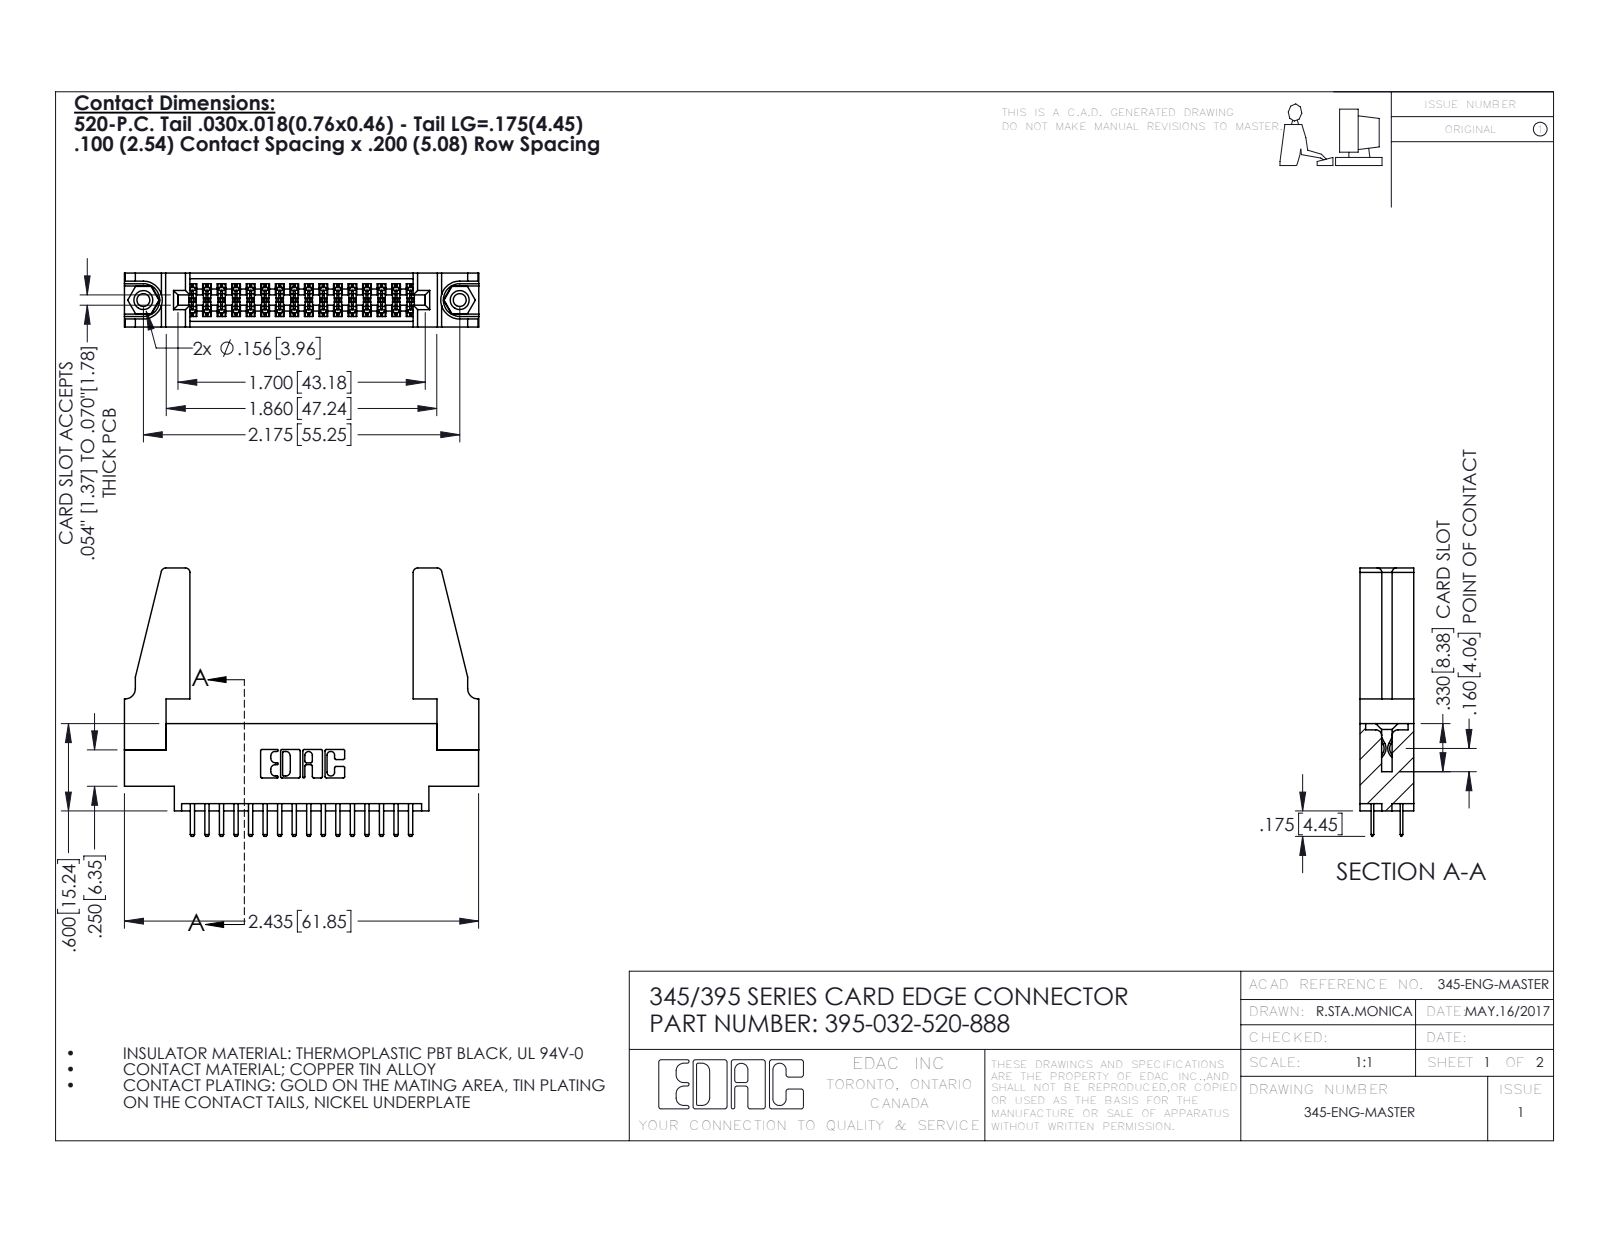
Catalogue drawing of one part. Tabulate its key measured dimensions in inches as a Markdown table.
| quantity | value |
| --- | --- |
| part name | 345-250-001_345-250-001-102; 345 Part_0.170 Offset - 0.156 Dia-TH; 345-292-001_345-293-120; 395-032-520-888 (+1 more) |
| STEP written by | SolidWorks 2016 (CONFIG_CONTROL_DESIGN) |
| units | inches |
| bodies | 37 solids, 1982 faces (1276 planar, 690 cylindrical, 16 other) |
| overall size | 2.436 × 1.845 × 0.37 |
| volume | 0.543 in³ |
| surface area | 17.16 in² |
| round holes (diameter × count) | 0.089 × 2, 0.125 × 2, 0.156 × 2, 0.064 × 1 |
| round bosses / shafts (diameter × count) | 0.155 × 2 |
| partial cylindrical surfaces (radius × count) | 0.006 × 48, 0.01 × 36, 0.01 × 22, 0.03 × 8, 0.007 × 6, 0.031 × 6, 0.026 × 3, 0.014 × 2 |
| main face-to-face distances | 0.37, 0.072, 0.298, 0.2, 0.098, 0.272, 0.025, 0.225, 0.022, 0.175 |
| hole center spacings | 0.27, 1.942, 2.175 |
